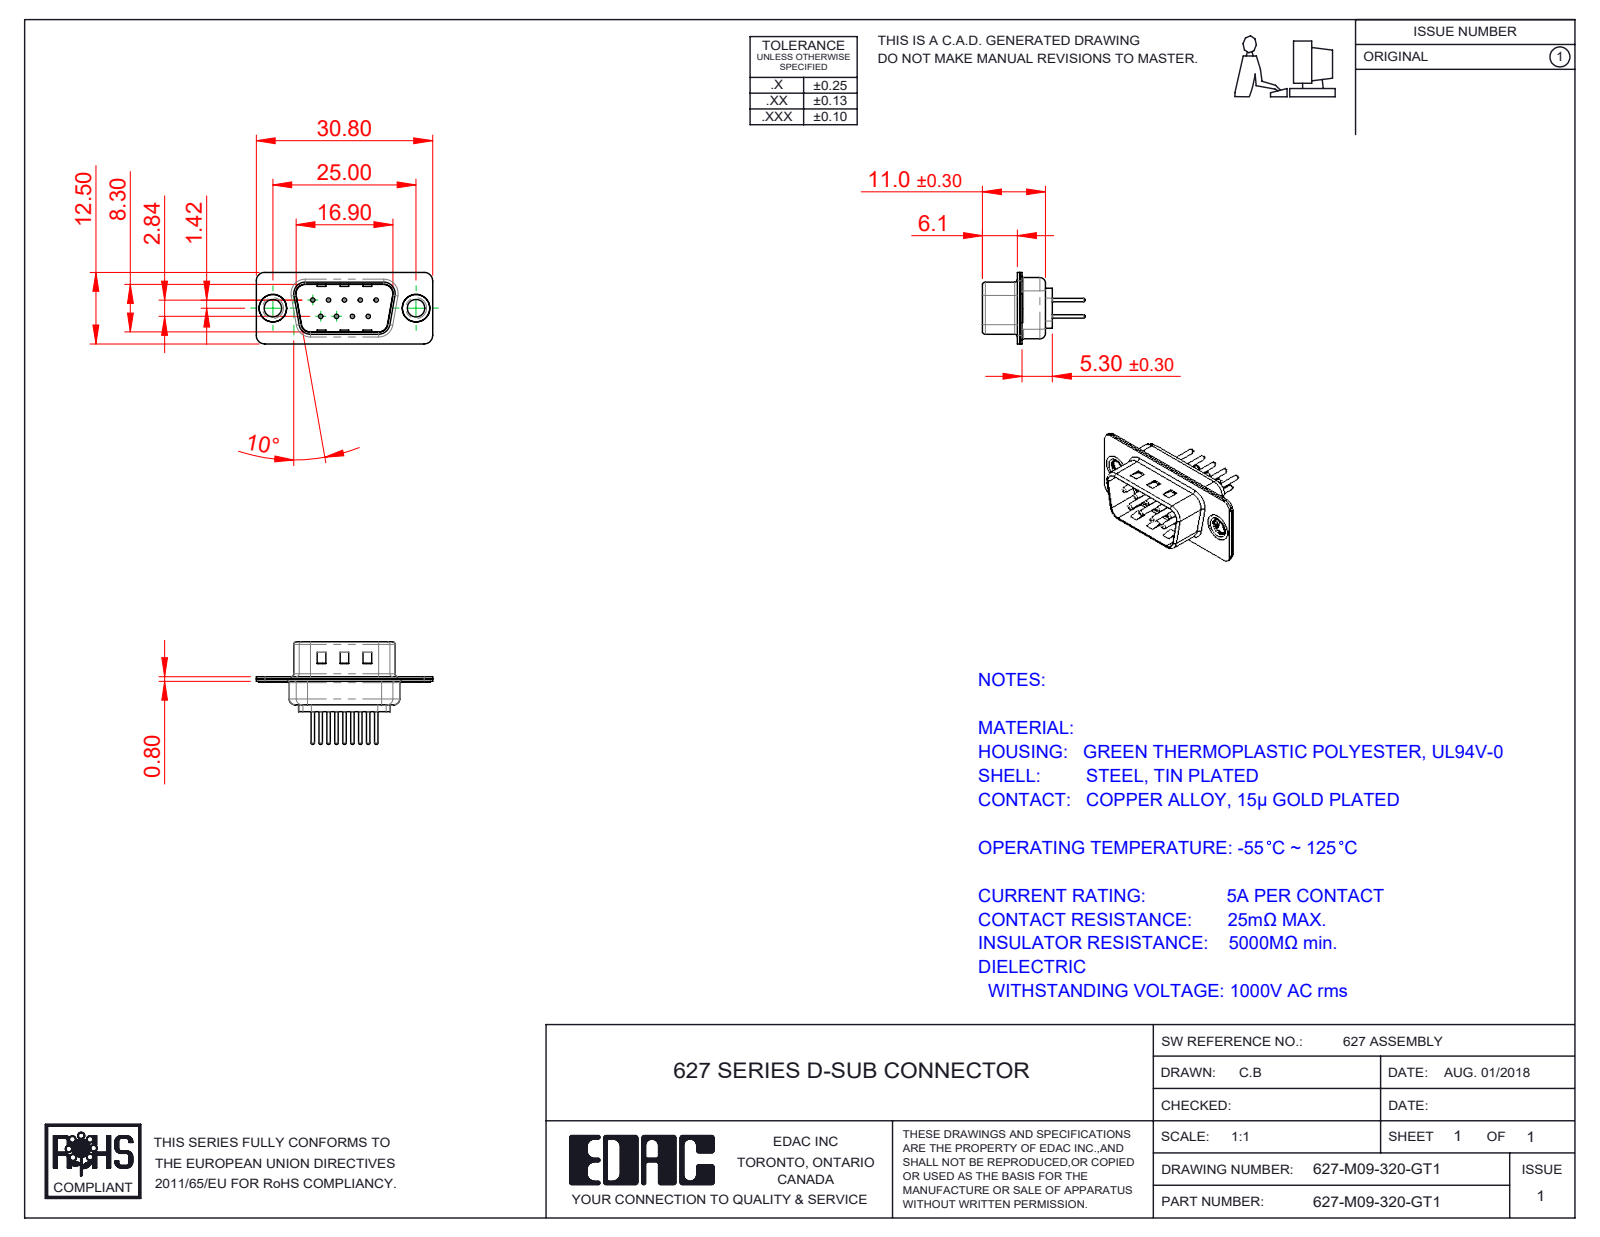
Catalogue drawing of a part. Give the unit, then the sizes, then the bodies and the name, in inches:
Units: inches
Overall size (bounding box): 1.213 × 0.705 × 0.492
Round holes (diameter × count): ⌀0.03 ×9, ⌀0.063 ×9, ⌀0.079 ×9, ⌀0.12 ×2, ⌀0.157 ×2, ⌀0.189 ×2
Round bosses / shafts (diameter × count): ⌀0.059 ×9, ⌀0.024 ×9, ⌀0.197 ×2, ⌀0.193 ×2, ⌀0.14 ×2
Partial cylindrical surfaces — rounded edges, fillets, slot ends (radius × count): R0.059 ×16, R0.079 ×12, R0.02 ×8, R0.063 ×8, R0.01 ×4, R0.024 ×4, R0.026 ×4, R0.035 ×4
Main face-to-face distances: 0.016, 0.031, 0.374, 0.358, 0.343, 0.026, 0.39, 0.047, 0.24, 0.224
Hole centre spacings: 0.124, 0.109, 0.218, 0.198, 0.198, 0.327, 0.28, 0.294
Volume: 0.075 in³ · Surface area: 5.315 in²
Bodies: 14 solids, 611 faces (170 planar, 239 cylindrical, 202 other)
Part name (STEP PRODUCT): 627M Shell Front_09 Contacts; 627M Thru Hole Rivet; 627-M09-320-GT1; 627M Housing_09 Contacts (+3 more)
STEP written by: SolidWorks 2020 (CONFIG_CONTROL_DESIGN)
